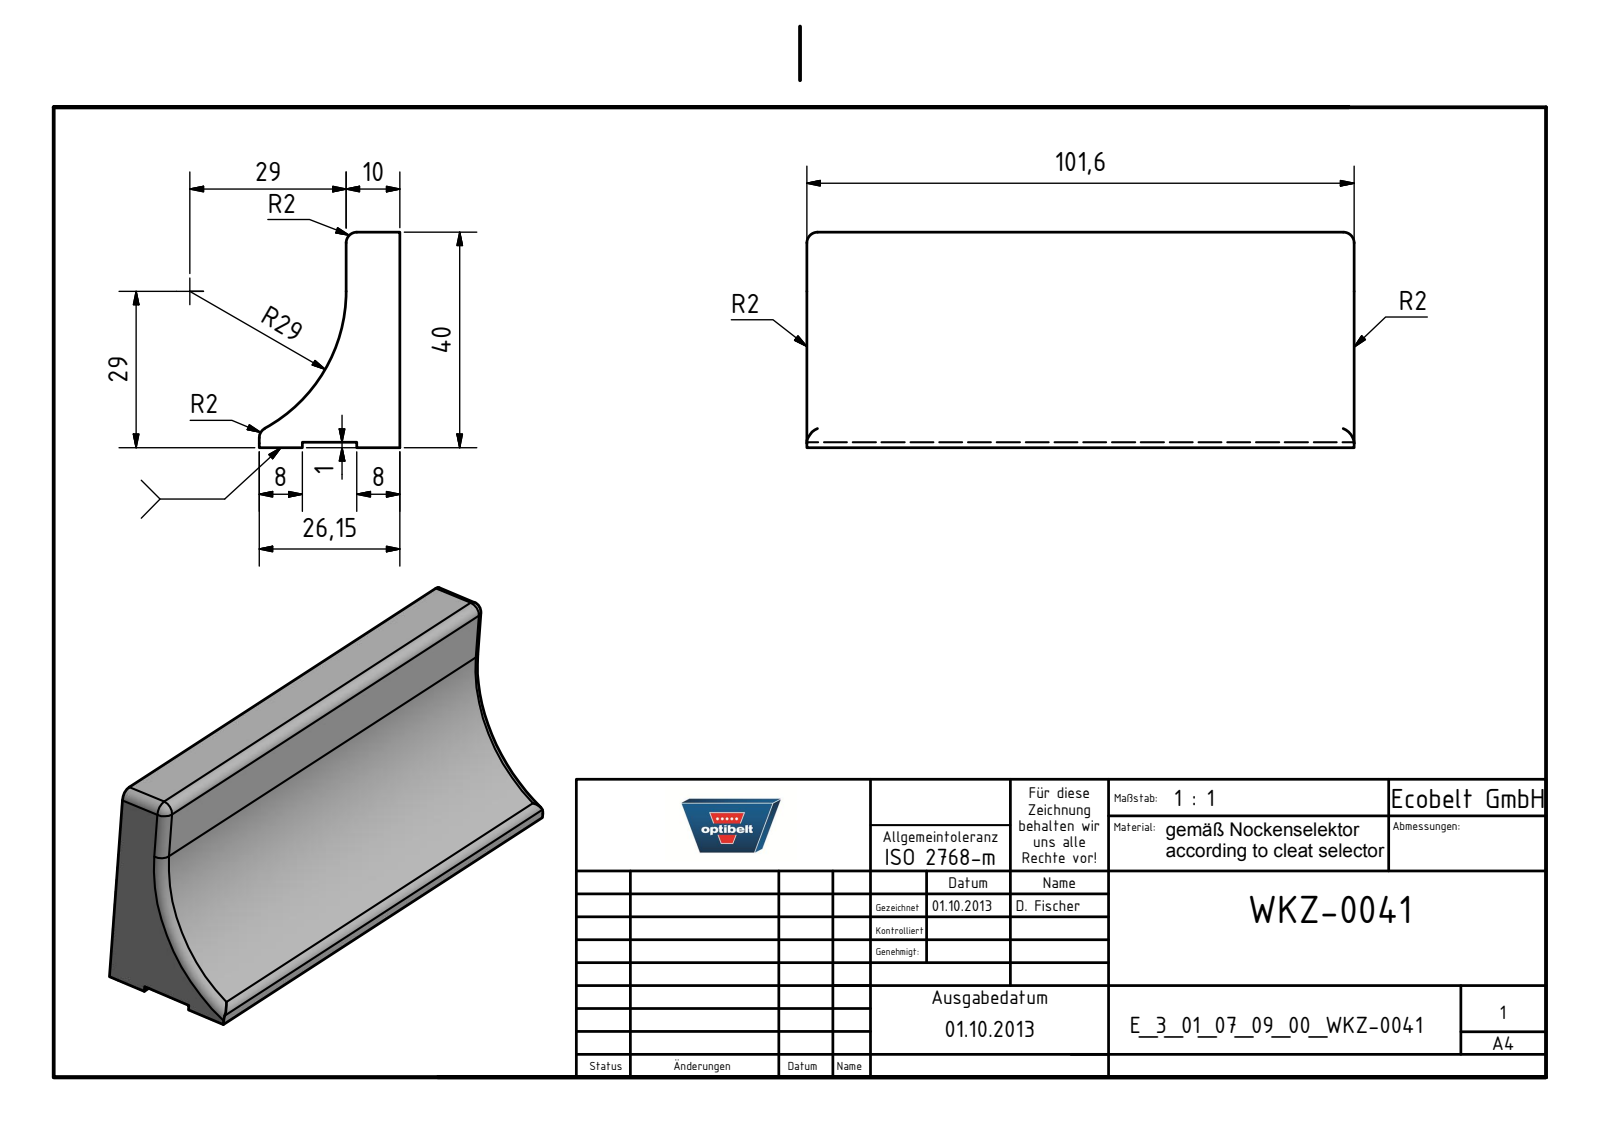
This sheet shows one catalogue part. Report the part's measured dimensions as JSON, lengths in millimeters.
{"part_name": "E_3_01_07_09_00_WKZ-0041", "step_written_by": "Autodesk Inventor 2021 (AUTOMOTIVE_DESIGN)", "units": "millimeters", "bodies": {"solids": 1, "faces": 22, "planar": 11, "cylindrical": 7, "other": 4}, "overall_size": [101.6, 40, 26.15], "volume_mm3": 56466, "surface_area_mm2": 13547, "partial_cylinders_radius": [[2, 6], [29, 1]], "face_to_face_distances": [1, 10, 40, 39, 101.6, 8, 18.15, 16.15, 26.15, 2]}
